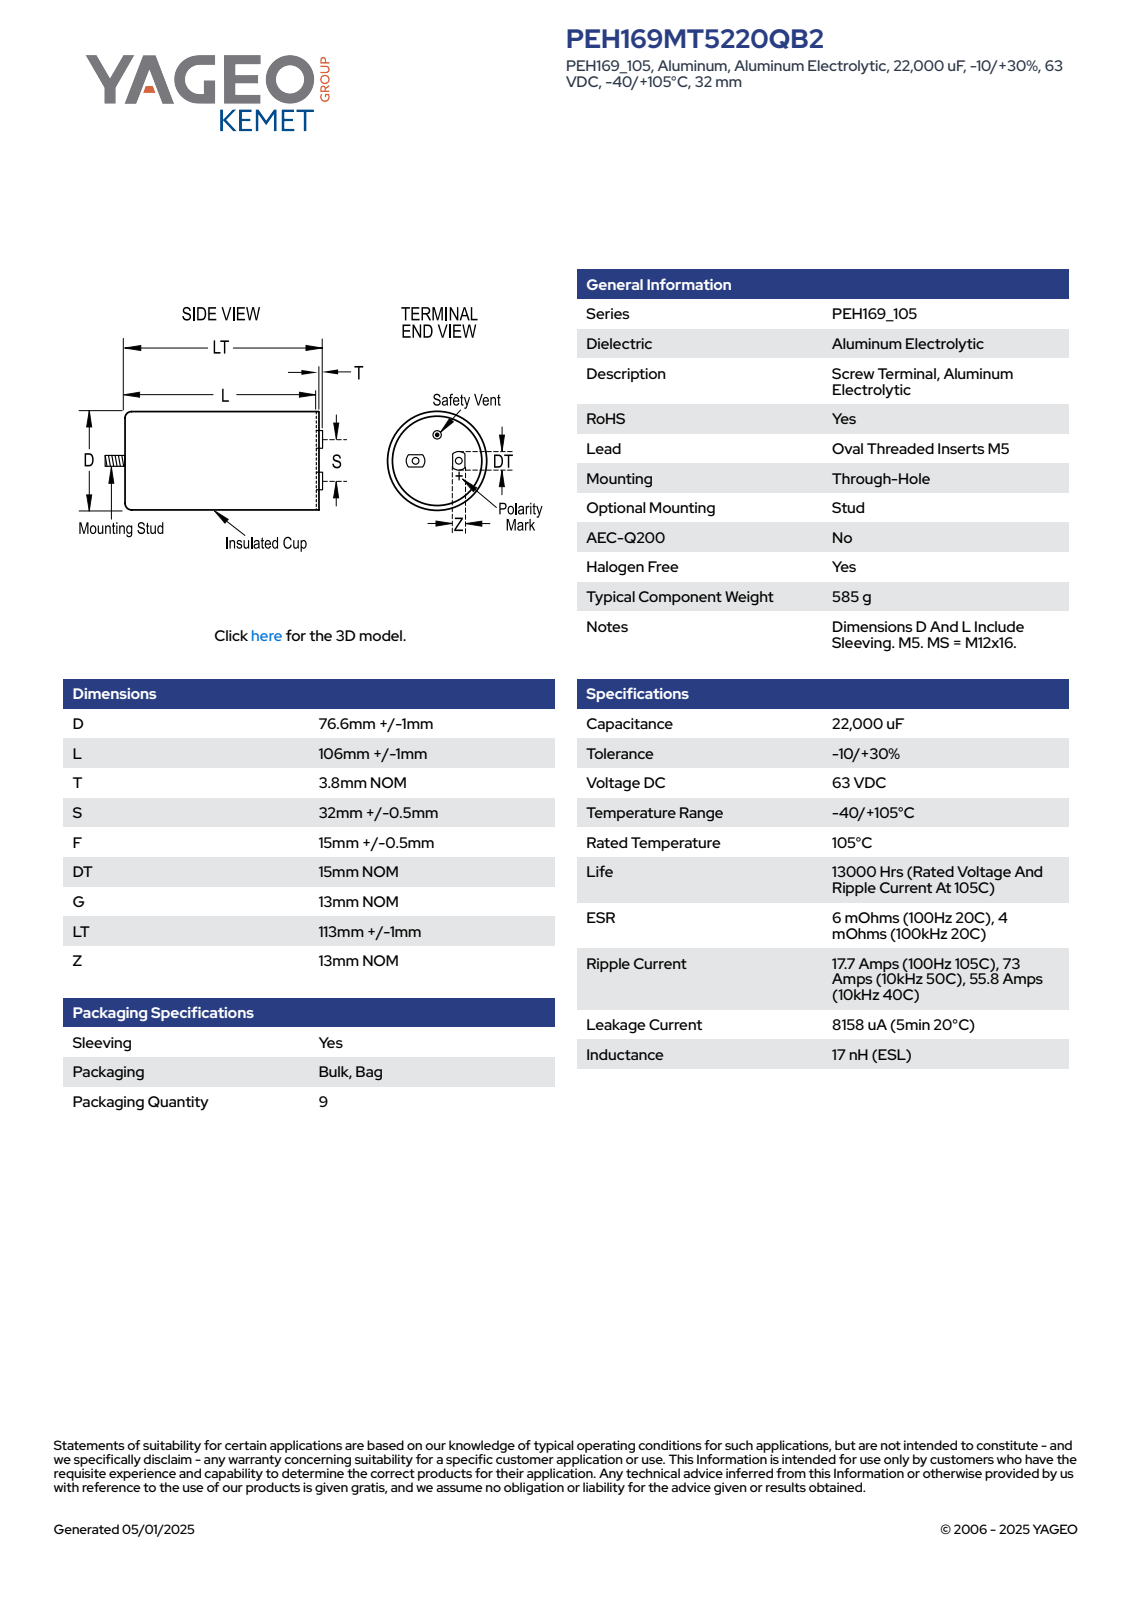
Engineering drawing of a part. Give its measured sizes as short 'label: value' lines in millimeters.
name: Stud; Oval_Terminal_22; CARCS_D77.6L107S32T3.8; Can_22
written by: SolidWorks 2014 (AUTOMOTIVE_DESIGN)
unit: mm
bodies: 4 solids, 185 faces (70 planar, 83 cylindrical, 32 other)
size: 130 × 77.6 × 77.6
volume: 510 336 mm³; area: 39 489 mm²
holes: 2× ⌀4.02, 1× ⌀75.6
bosses: 2× ⌀7.5, 1× ⌀77.6, 1× ⌀12, 1× ⌀11.6
rounds: 2× R7.5, 1× R38.79
face distances: 107, 7, 114, 3.2, 3.8, 110.2, 5, 130, 126.2, 123
hole spacings: 16, 32
